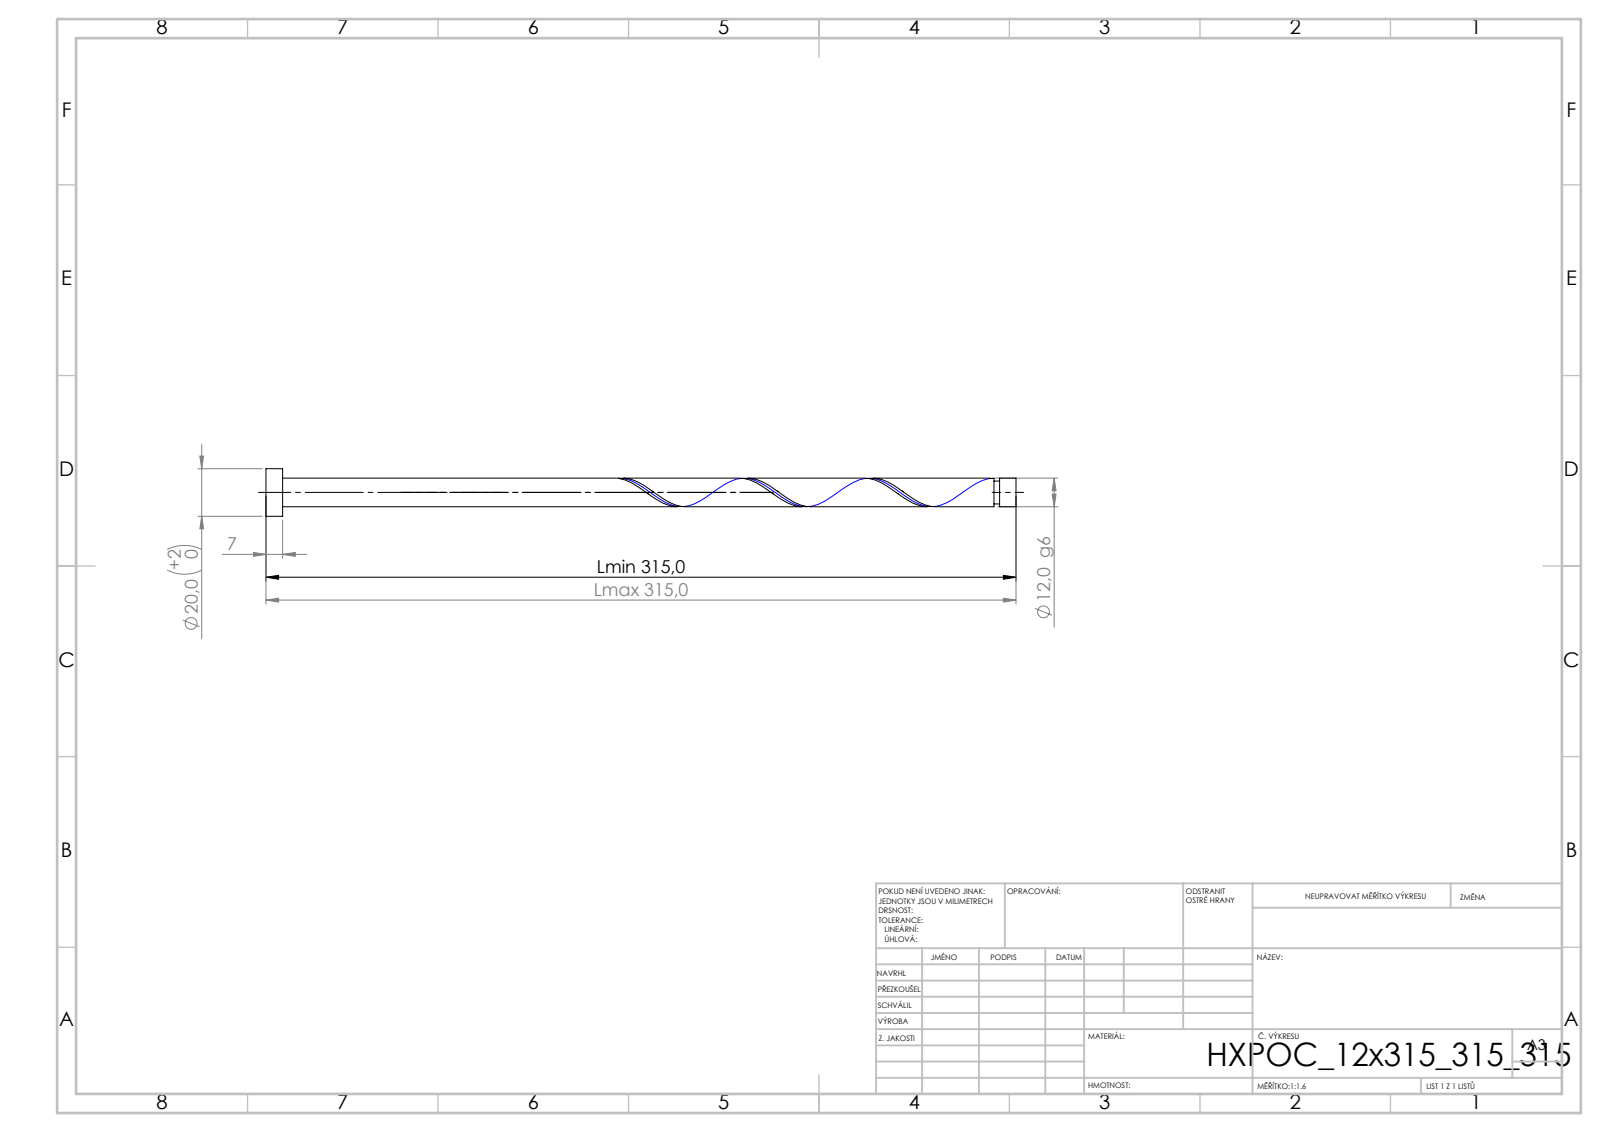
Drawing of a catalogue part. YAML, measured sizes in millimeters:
step_written_by: "SolidWorks 2019 (CONFIG_CONTROL_DESIGN)"
units: millimeters
bodies: {solids: 1, faces: 21, planar: 6, cylindrical: 14, other: 1}
overall_size: [315, 20, 20]
volume: 36594
surface_area: 12982
round_bosses_or_shafts:
  - {diameter: 20, count: 1}
  - {diameter: 12, count: 1}
  - {diameter: 9.6, count: 1}
face_to_face_distances: [7, 315, 308, 308.13, 301.13, 6.87, 305.73, 298.73, 2.4, 9.27]
